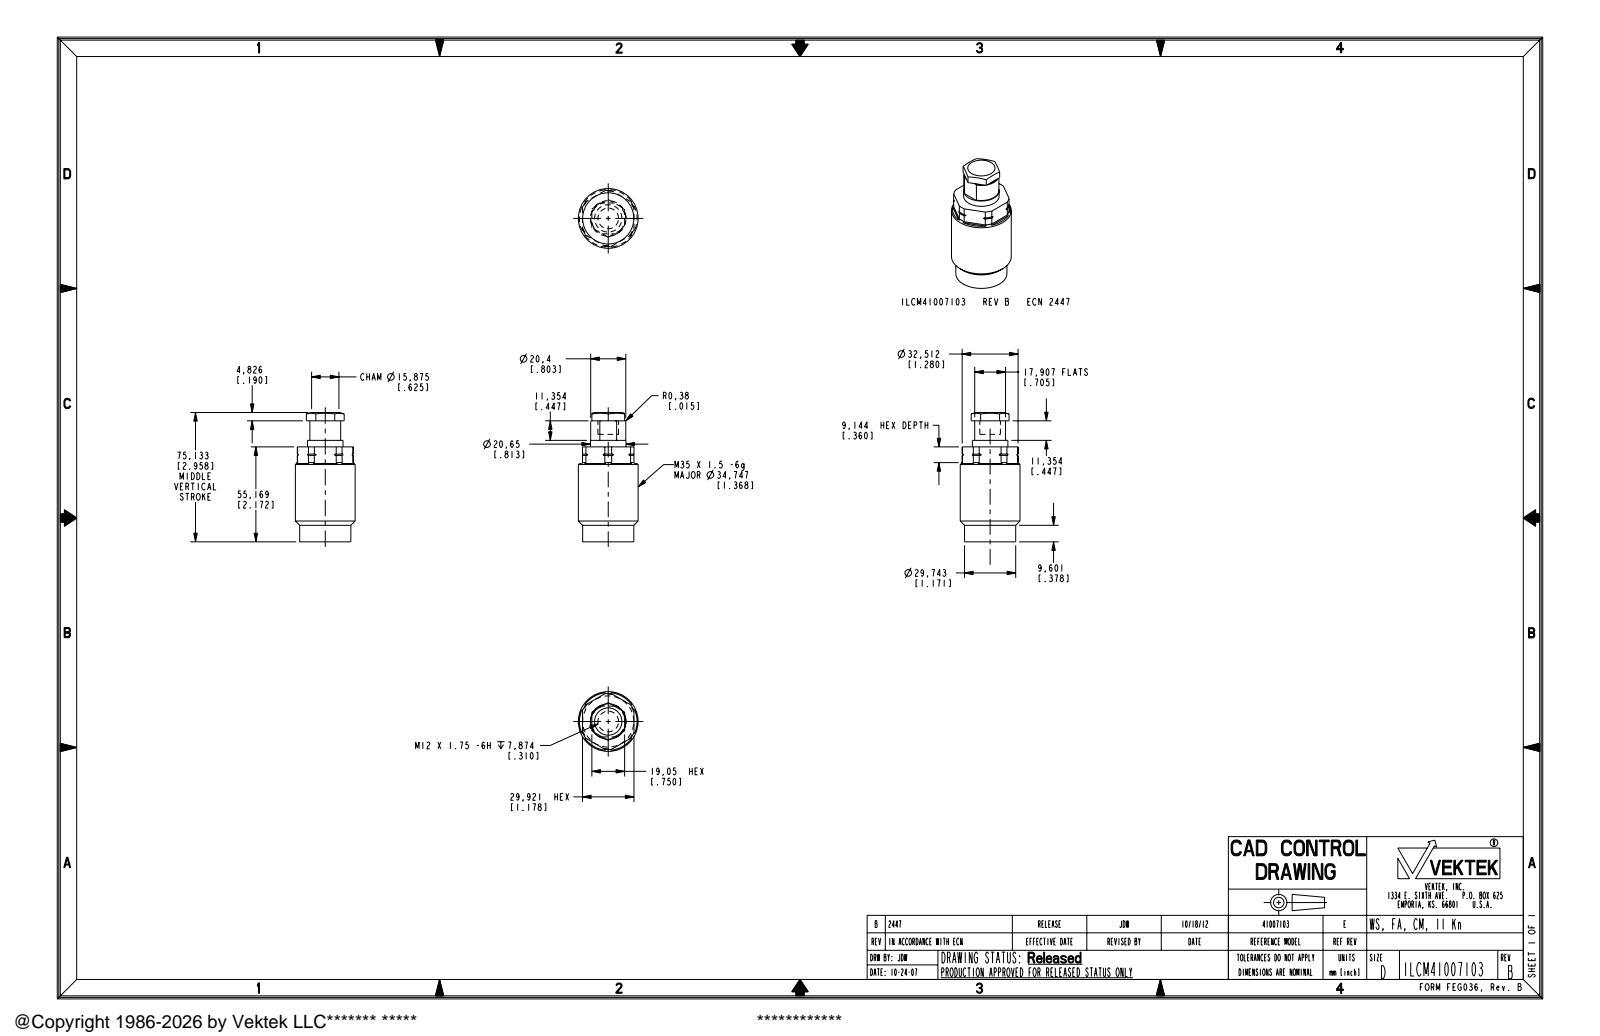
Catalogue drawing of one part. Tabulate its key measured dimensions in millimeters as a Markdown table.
| quantity | value |
| --- | --- |
| part name | ILCM41007103 |
| STEP written by | PRO/ENGINEER BY PARAMETRIC TECHNOLOGY CORPORATION, 2007460 (AUTOMOTIVE_DESIGN_CC2) |
| units | millimeters |
| bodies | 1 solid, 83 faces (39 planar, 28 cylindrical, 16 other) |
| overall size | 75.13 × 34.75 × 34.75 |
| volume | 53 139 mm³ |
| surface area | 9 272 mm² |
| round holes (diameter × count) | 11.99 × 1 |
| round bosses / shafts (diameter × count) | 34.75 × 1, 29.74 × 1, 20.65 × 1 |
| partial cylindrical surfaces (radius × count) | 0.51 × 6, 10.2 × 1, 16.26 × 1 |
| main face-to-face distances | 55.17, 29.92, 75.13, 19.96, 5.44, 24.48, 70.31, 15.14, 4.82, 62.43 |
